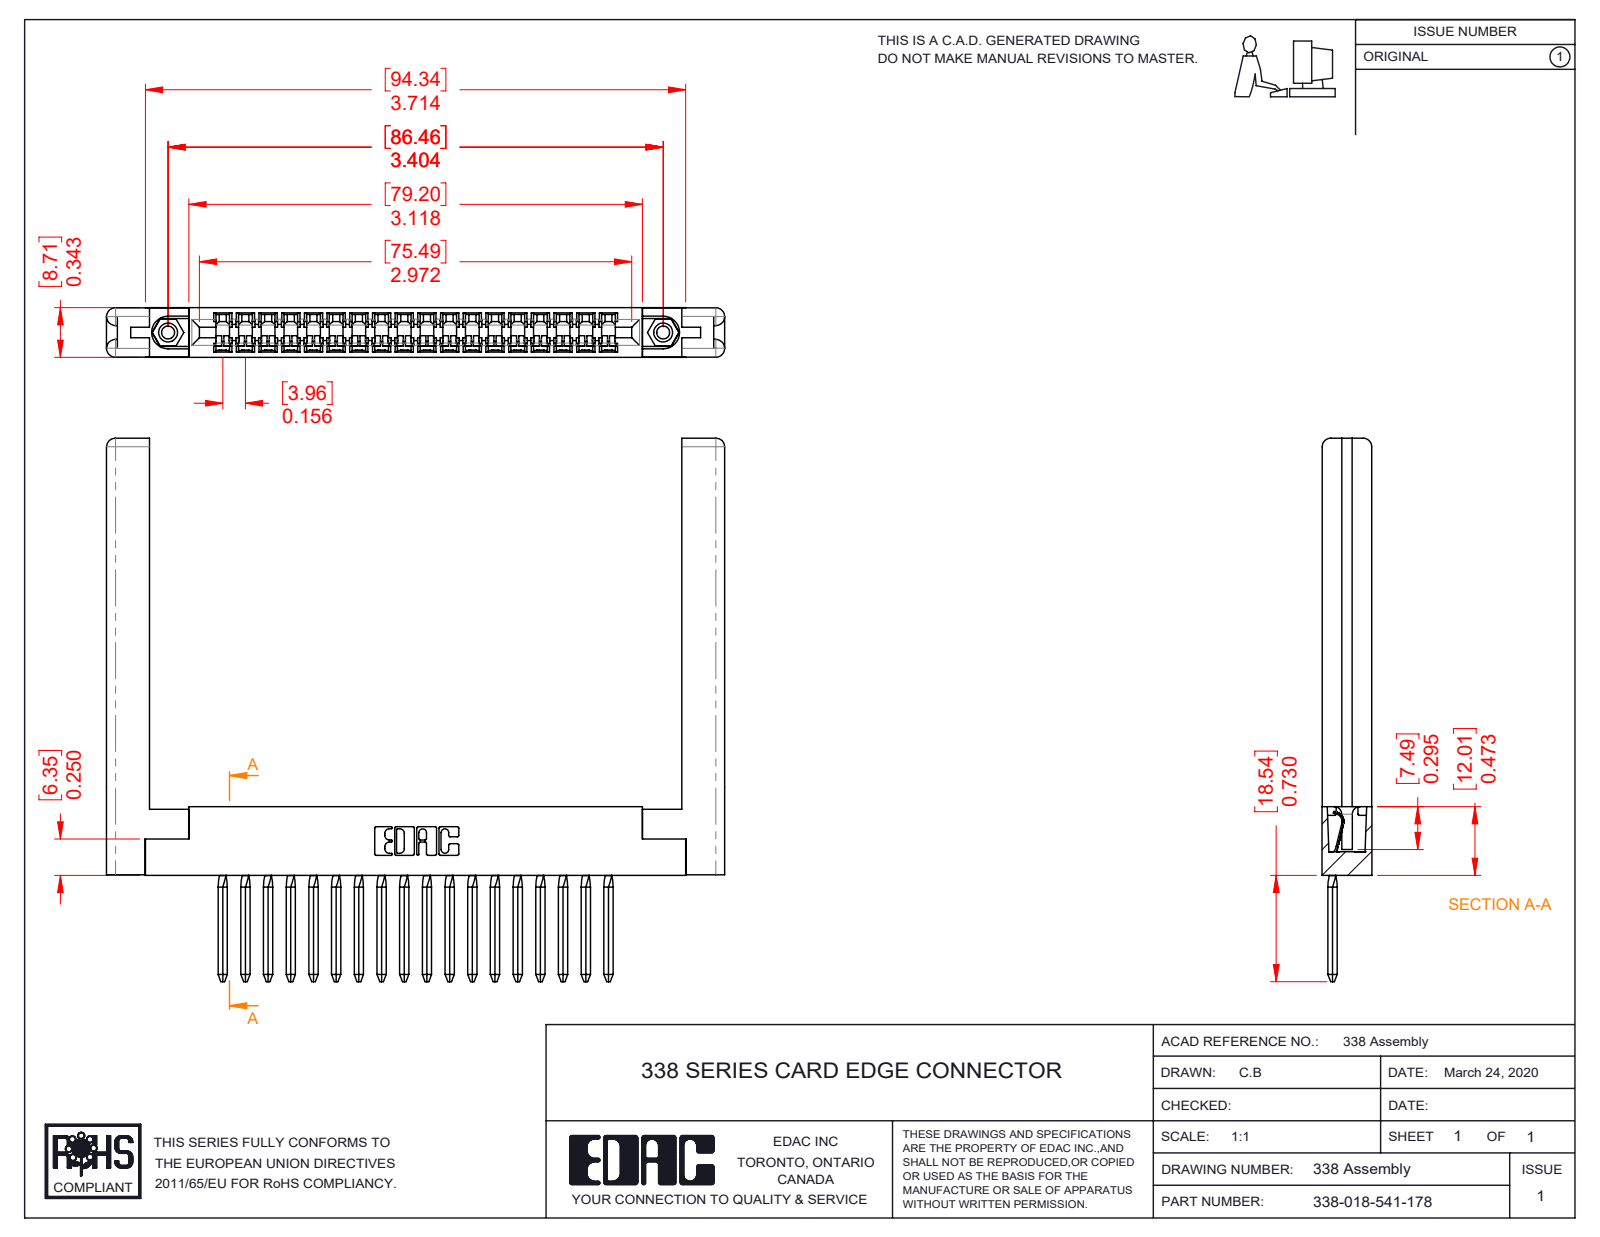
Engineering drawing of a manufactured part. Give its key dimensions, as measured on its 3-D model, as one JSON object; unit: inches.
{"part_name": "338-018-541-178; 345-250-001_345-250-001-102; 307-220-058; 338-290-001_541 (+1 more)", "step_written_by": "SolidWorks 2016 (CONFIG_CONTROL_DESIGN)", "units": "inches", "bodies": {"solids": 23, "faces": 1910, "planar": 1304, "cylindrical": 510, "other": 96}, "overall_size": [4.25, 3.735, 0.343], "volume_in3": 0.925, "surface_area_in2": 26.5, "round_holes": [[0.089, 2], [0.125, 2], [0.156, 2]], "round_bosses_or_shafts": [[0.155, 2]], "partial_cylinders_radius": [[0.025, 74], [0.01, 22], [0.008, 18], [0.055, 15], [0.067, 15], [0.1, 14], [0.061, 8], [0.007, 6]], "face_to_face_distances": [0.341, 0.343, 0.34, 0.136, 0.207, 0.134, 0.206, 0.22, 3.66, 0.071], "hole_center_spacings": [3.404]}
